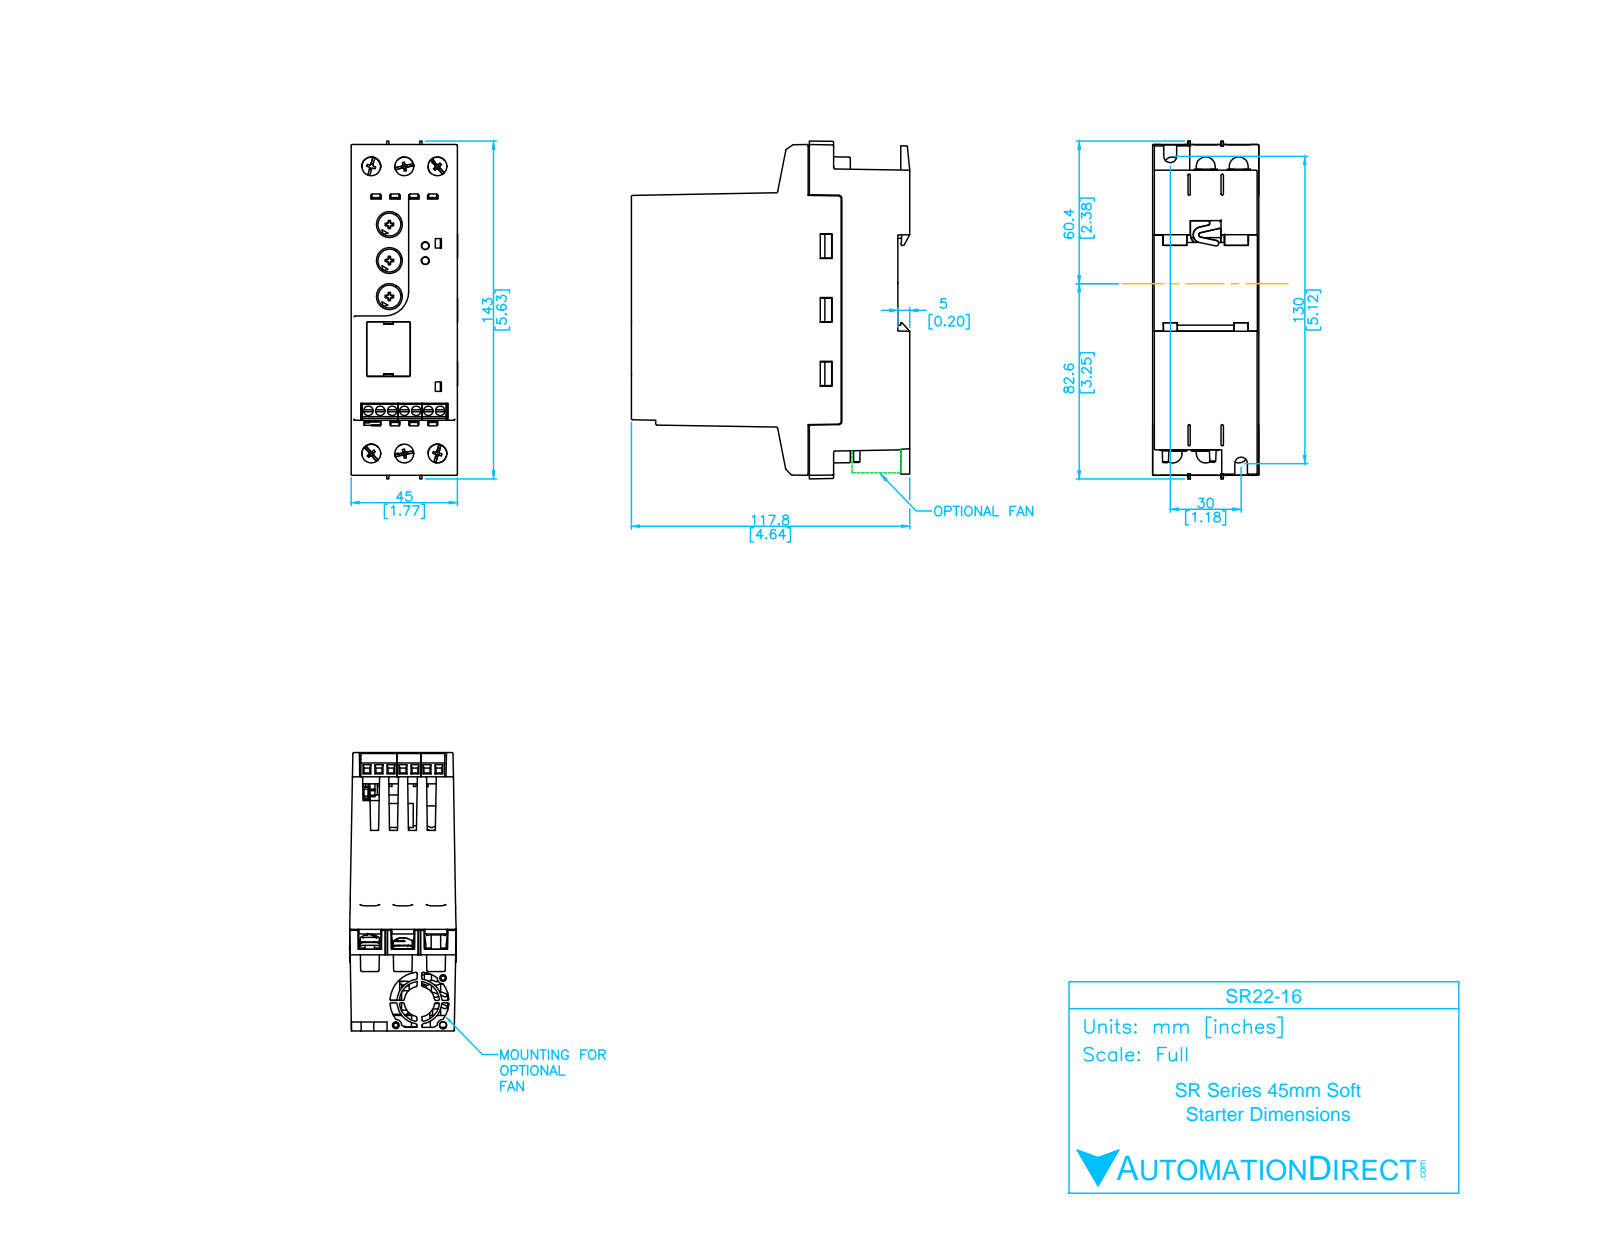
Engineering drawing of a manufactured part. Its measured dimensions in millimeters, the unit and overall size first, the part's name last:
Units: millimetres
Overall size (bounding box): 144 × 117.8 × 45.64
Round holes (diameter × count): ⌀9.5 ×6, ⌀3.5 ×5, ⌀11.3 ×3, ⌀4 ×2
Round bosses / shafts (diameter × count): ⌀10.44 ×3
Partial cylindrical surfaces — rounded edges, fillets, slot ends (radius × count): R0.5 ×36, R4.88 ×6, R1 ×2, R2.75 ×2, R10 ×1
Main face-to-face distances: 45, 44.98, 44.96, 117.8, 0.5, 5.14, 112.66, 1.5, 116.3, 111.16
Hole centre spacings: 5.25, 13, 123.69, 10.5, 123, 15, 15.75, 26
Volume: 572 724 mm³ · Surface area: 56 020 mm²
Bodies: 1 solid, 567 faces (437 planar, 98 cylindrical, 32 other)
Part name (STEP PRODUCT): SR22-016
STEP written by: SolidWorks 2013 (AUTOMOTIVE_DESIGN)
